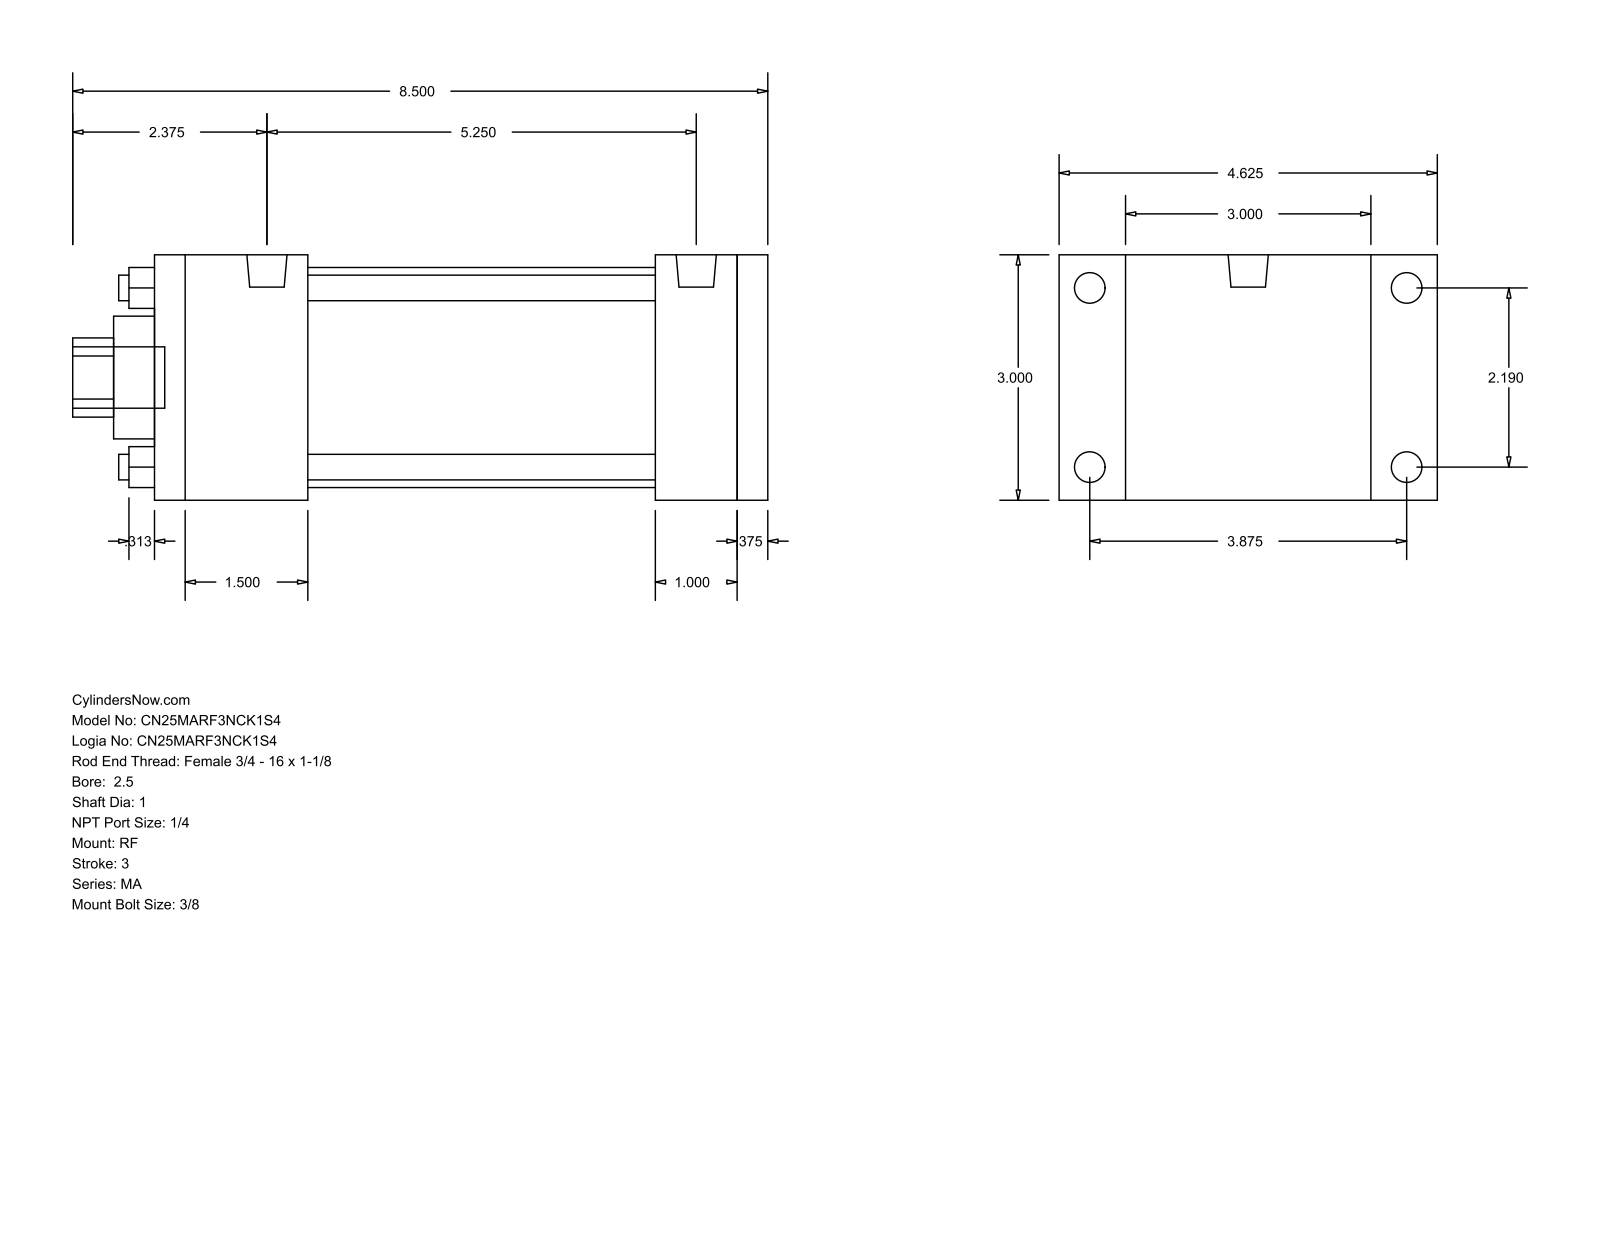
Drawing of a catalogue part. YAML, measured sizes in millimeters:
part_name: "MA_RF__0250_1"
step_written_by: "GSSL Pune (CONFIG_CONTROL_DESIGN)"
units: millimeters
bodies: {solids: 0, faces: 92, planar: 64, cylindrical: 28, other: 0}
overall_size: [215.9, 117.47, 76.2]
round_holes:
  - {diameter: 7.94, count: 4}
  - {diameter: 25.4, count: 1}
  - {diameter: 38.1, count: 1}
  - {diameter: 68.33, count: 1}
round_bosses_or_shafts:
  - {diameter: 9.53, count: 4}
  - {diameter: 7.94, count: 4}
  - {diameter: 12.49, count: 2}
  - {diameter: 19.05, count: 1}
partial_cylinders:
  - {radius: 12.29, count: 1}
face_to_face_distances: [76.2, 190.5, 180.98, 9.52, 47.63, 155.57, 107.94, 133.35, 142.87, 25.41]
hole_center_spacings: [39.33, 55.62, 78.66]
